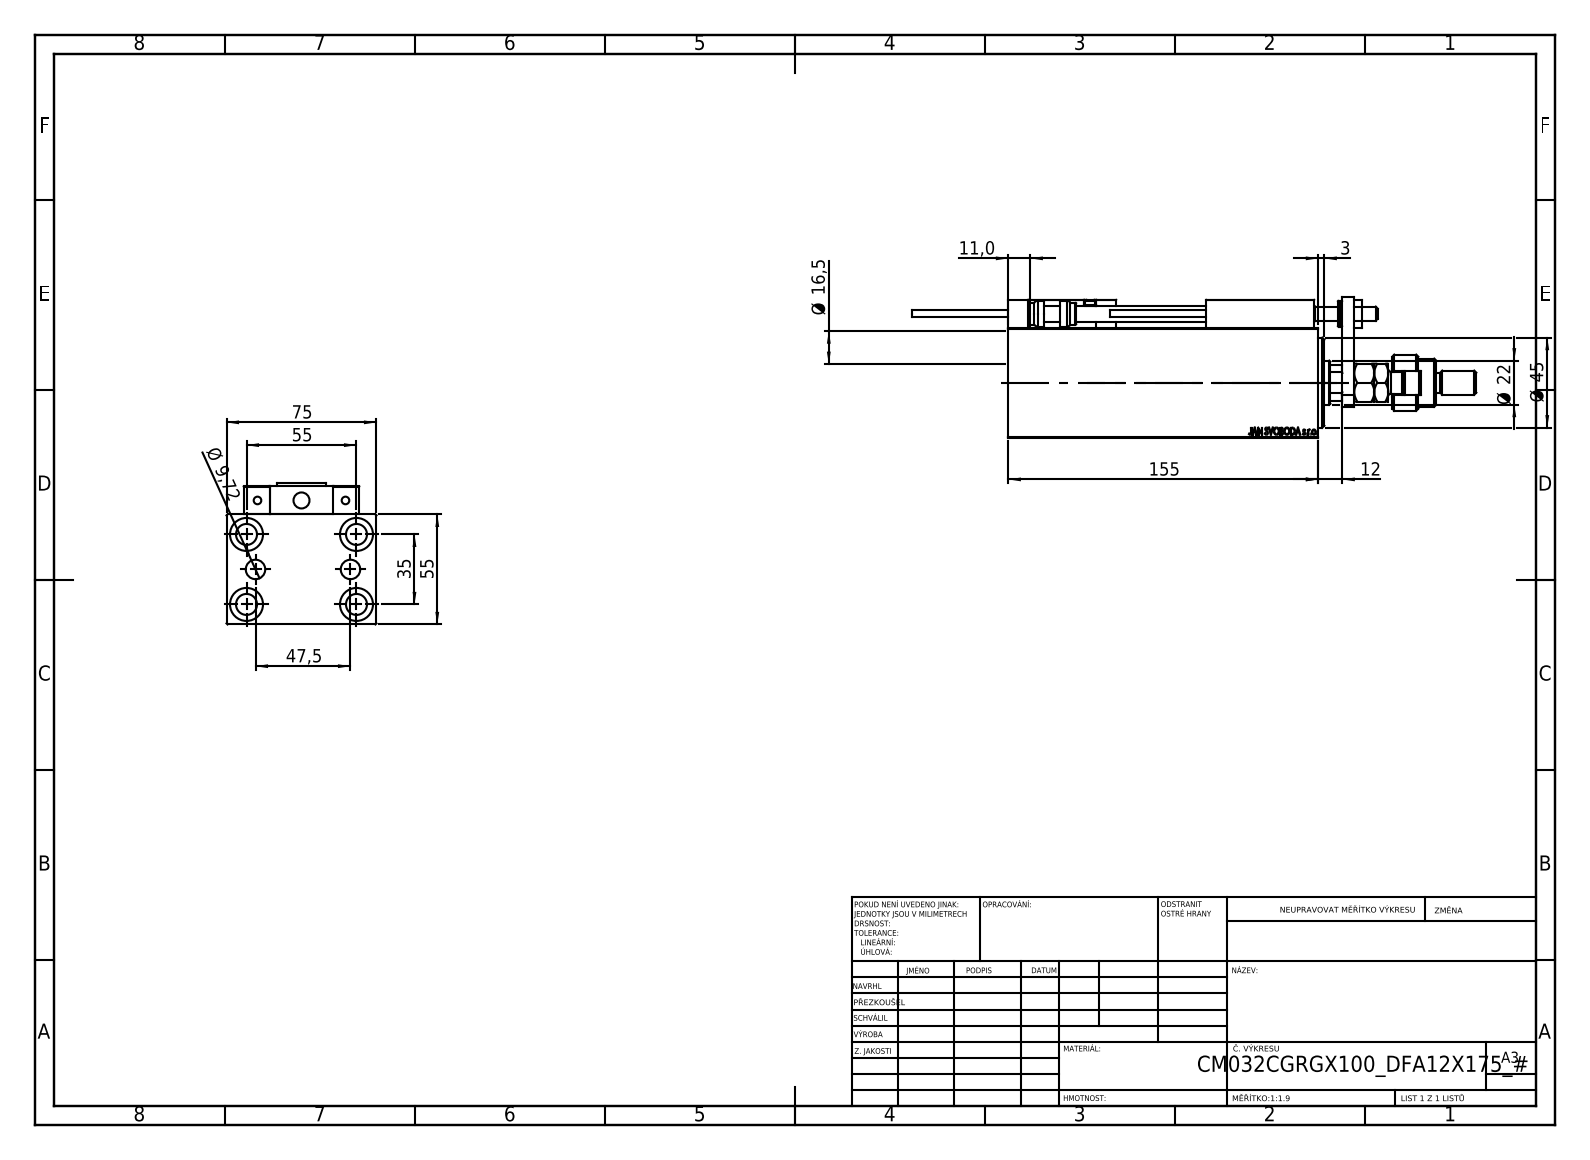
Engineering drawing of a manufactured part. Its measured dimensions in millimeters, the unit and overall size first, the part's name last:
Units: millimetres
Overall size (bounding box): 282 × 75 × 70.5
Round holes (diameter × count): ⌀8 ×5, ⌀10.5 ×5, ⌀16.5 ×5, ⌀3.2 ×4, ⌀4 ×4, ⌀5 ×2, ⌀9.72 ×2, ⌀7 ×1, ⌀22 ×1, ⌀25.5 ×1, ⌀32 ×1, ⌀34 ×1
Round bosses / shafts (diameter × count): ⌀11 ×2, ⌀5 ×2, ⌀3.8 ×2, ⌀28 ×1, ⌀24 ×1, ⌀18 ×1, ⌀13 ×1, ⌀12 ×1
Partial cylindrical surfaces — rounded edges, fillets, slot ends (radius × count): R0.3 ×30, R3 ×2, R9.75 ×1, R10.5 ×1
Main face-to-face distances: 55, 75, 14, 10, 12, 18, 25, 7, 6, 69
Hole centre spacings: 32.6, 11.37, 17.76, 18.07, 20, 29.59, 29.69, 32.33
Volume: 605 734 mm³ · Surface area: 137 831 mm²
Bodies: 25 solids, 1357 faces (586 planar, 193 cylindrical, 578 other)
Part name (STEP PRODUCT): ALLEN BOLT D8; ALLEN BOLT D5; MAGNET; KONCOVKA (+8 more)
STEP written by: SolidWorks 2019 (CONFIG_CONTROL_DESIGN)
